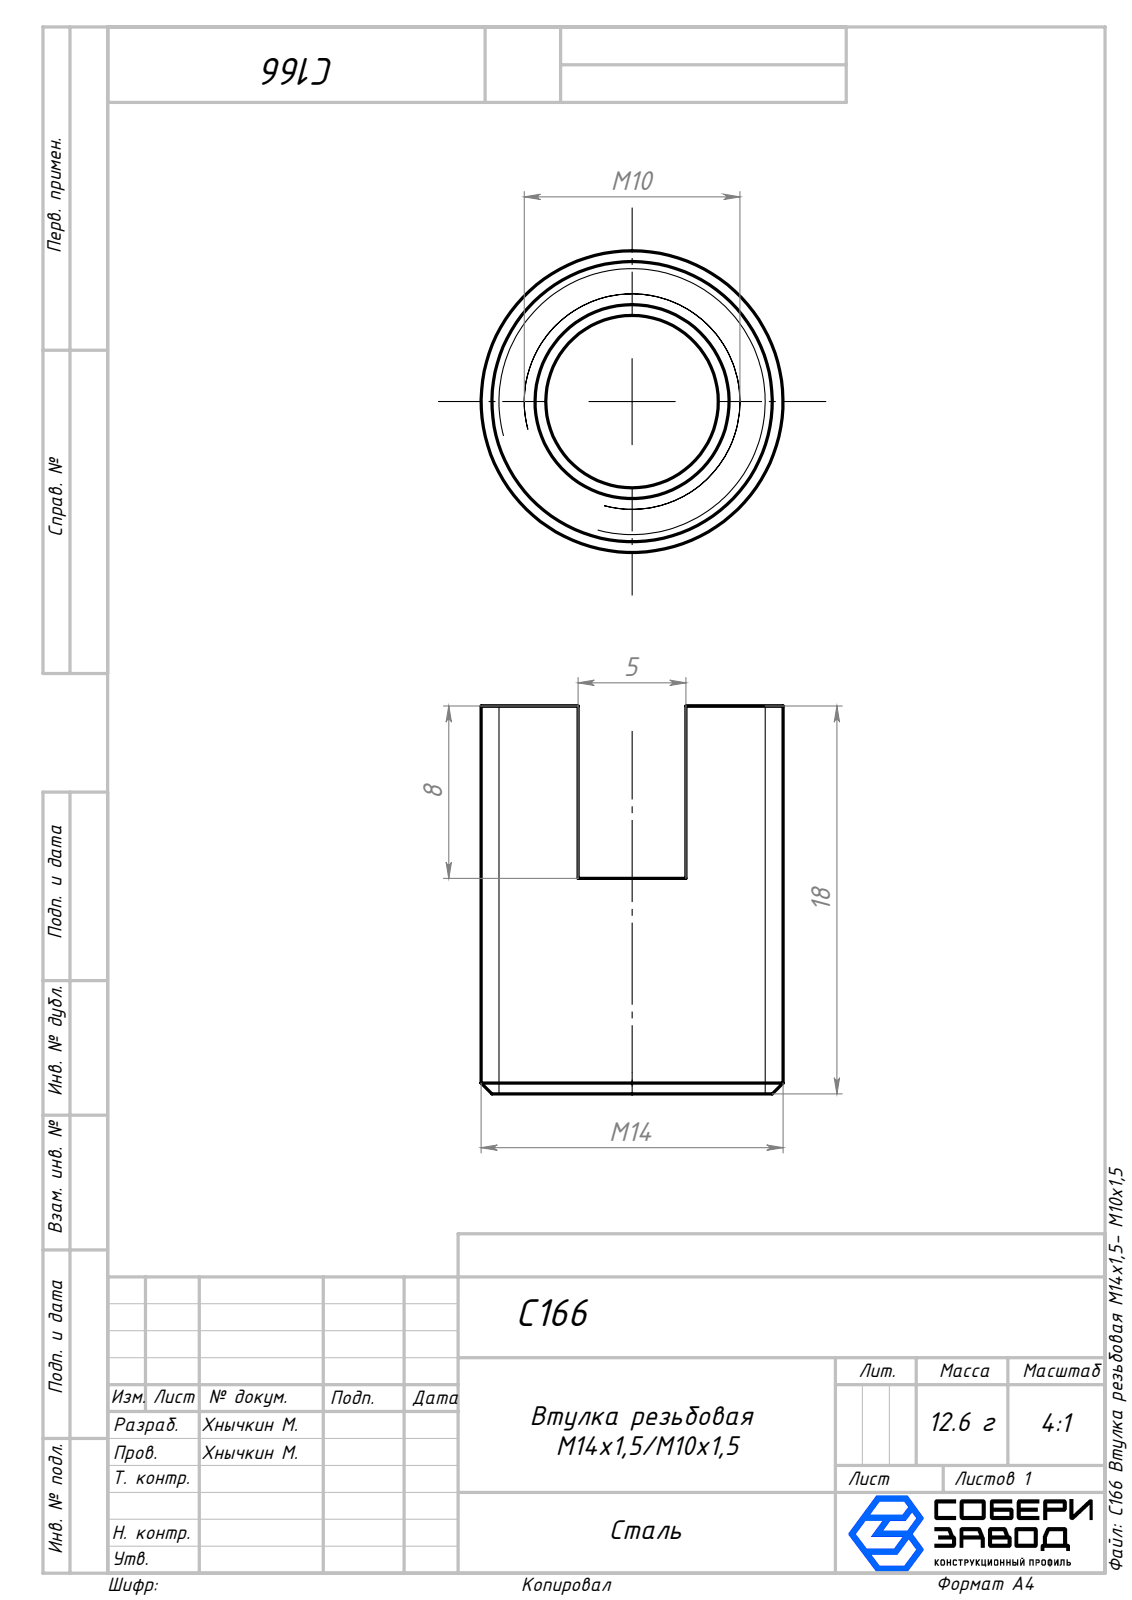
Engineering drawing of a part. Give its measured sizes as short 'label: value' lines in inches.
name: C166 Втулка резьбовая М14х1,5- М10х1,5
written by: SolidWorks 2026 (AUTOMOTIVE_DESIGN)
unit: in
bodies: 1 solid, 19 faces (9 planar, 4 cylindrical, 6 other)
size: 0.709 × 0.551 × 0.551
volume: 0.098 in³; area: 2.12 in²
holes: 1× ⌀0.315
bosses: 1× ⌀0.551
face distances: 0.709, 0.197, 0.394, 0.315
